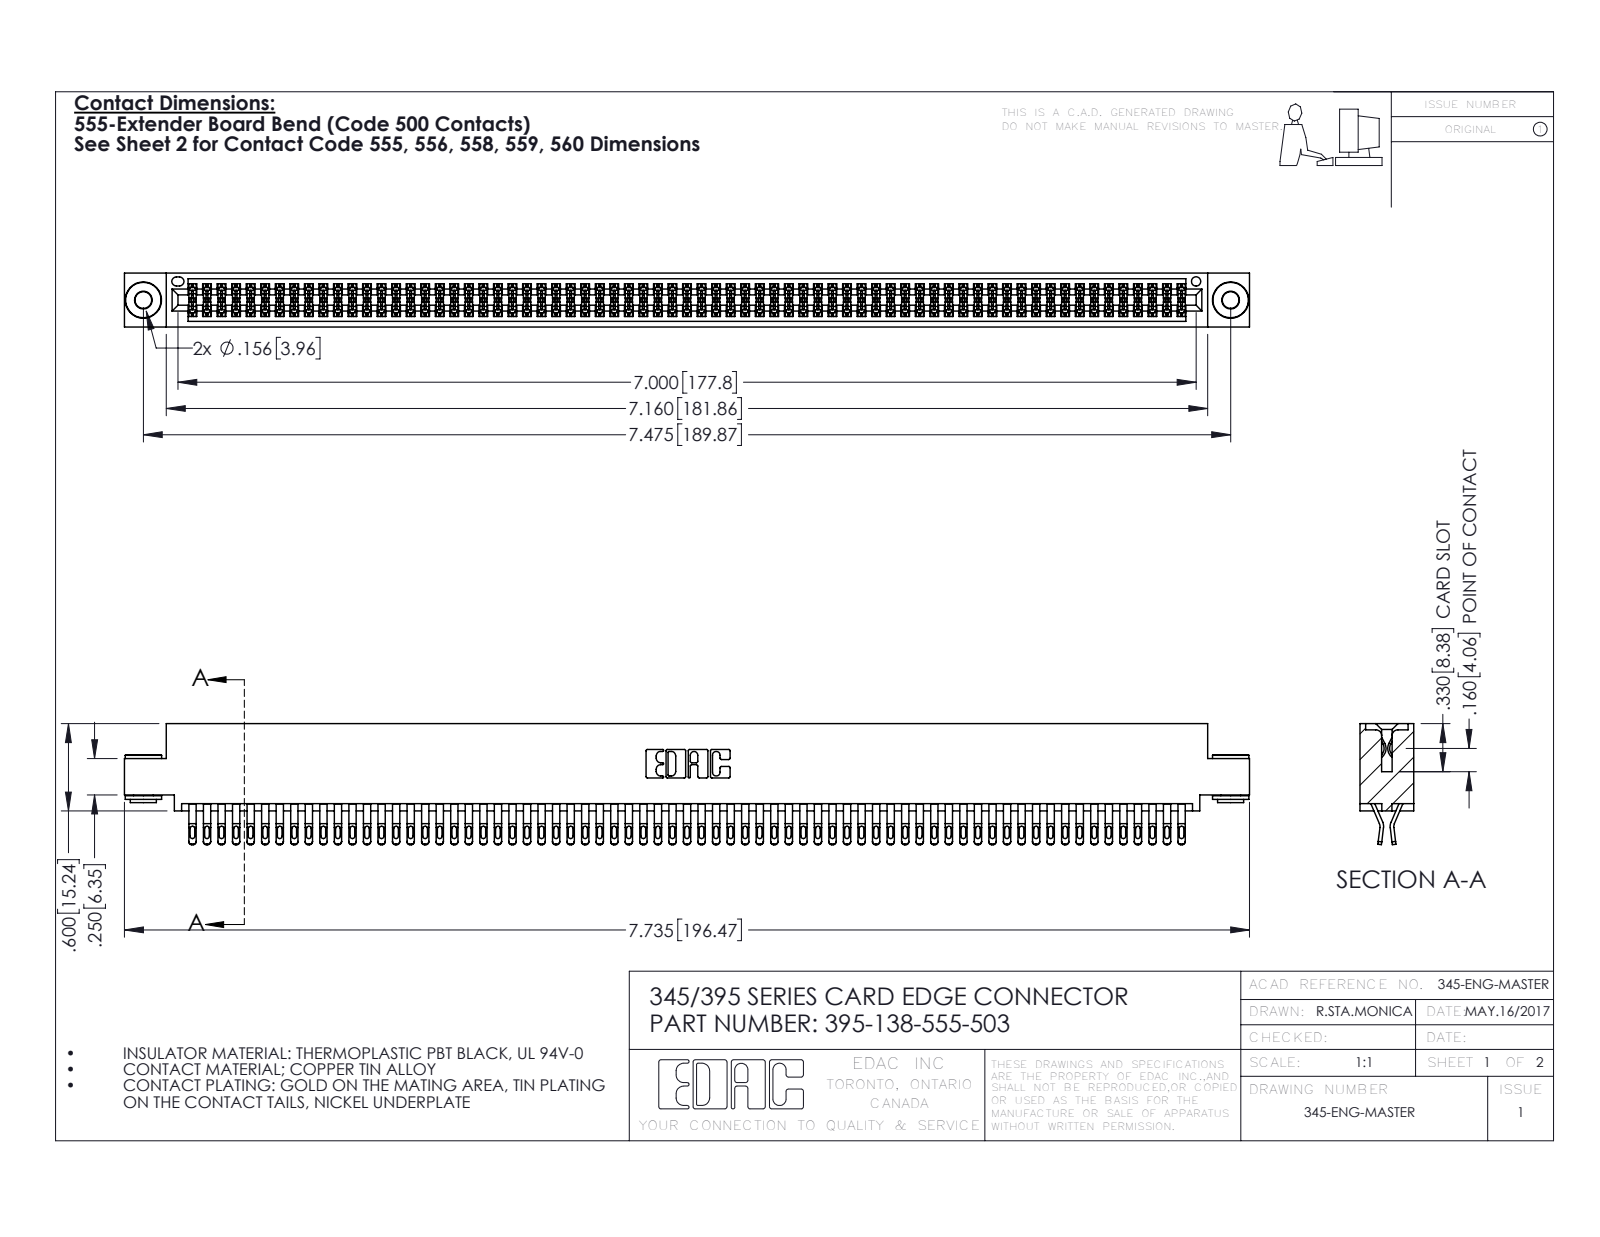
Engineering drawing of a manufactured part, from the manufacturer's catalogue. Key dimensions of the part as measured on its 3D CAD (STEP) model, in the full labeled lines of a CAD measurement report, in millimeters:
Part name (STEP PRODUCT): 395-138-555-503; 345-292-001_555 Tail; 345-250-002_345-250-002-102; 345 Part_0.110 Offset - 0.156 Dia-TH
STEP written by: SolidWorks 2016 (CONFIG_CONTROL_DESIGN)
Units: millimetres
Bodies: 141 solids, 7896 faces (4372 planar, 3516 cylindrical, 8 other)
Overall size (bounding box): 196.5 × 21.1 × 9.4
Volume: 19 680 mm³ · Surface area: 31 300 mm²
Round holes (diameter × count): ⌀2.9 ×2, ⌀4 ×2, ⌀1.6 ×1
Round bosses / shafts (diameter × count): ⌀6.4 ×2, ⌀4.6 ×2, ⌀3.5 ×2
Partial cylindrical surfaces — rounded edges, fillets, slot ends (radius × count): R0.4 ×345, R0.5 ×276, R0.2 ×207, R0.3 ×22, R0.2 ×6, R0.8 ×6, R0.7 ×3, R0.3 ×2
Main face-to-face distances: 1.8, 7.6, 0.6, 9.4, 5.1, 2.5, 6.9, 5.7, 4.4, 3.8
Hole centre spacings: 6.9, 183.9, 189.9
